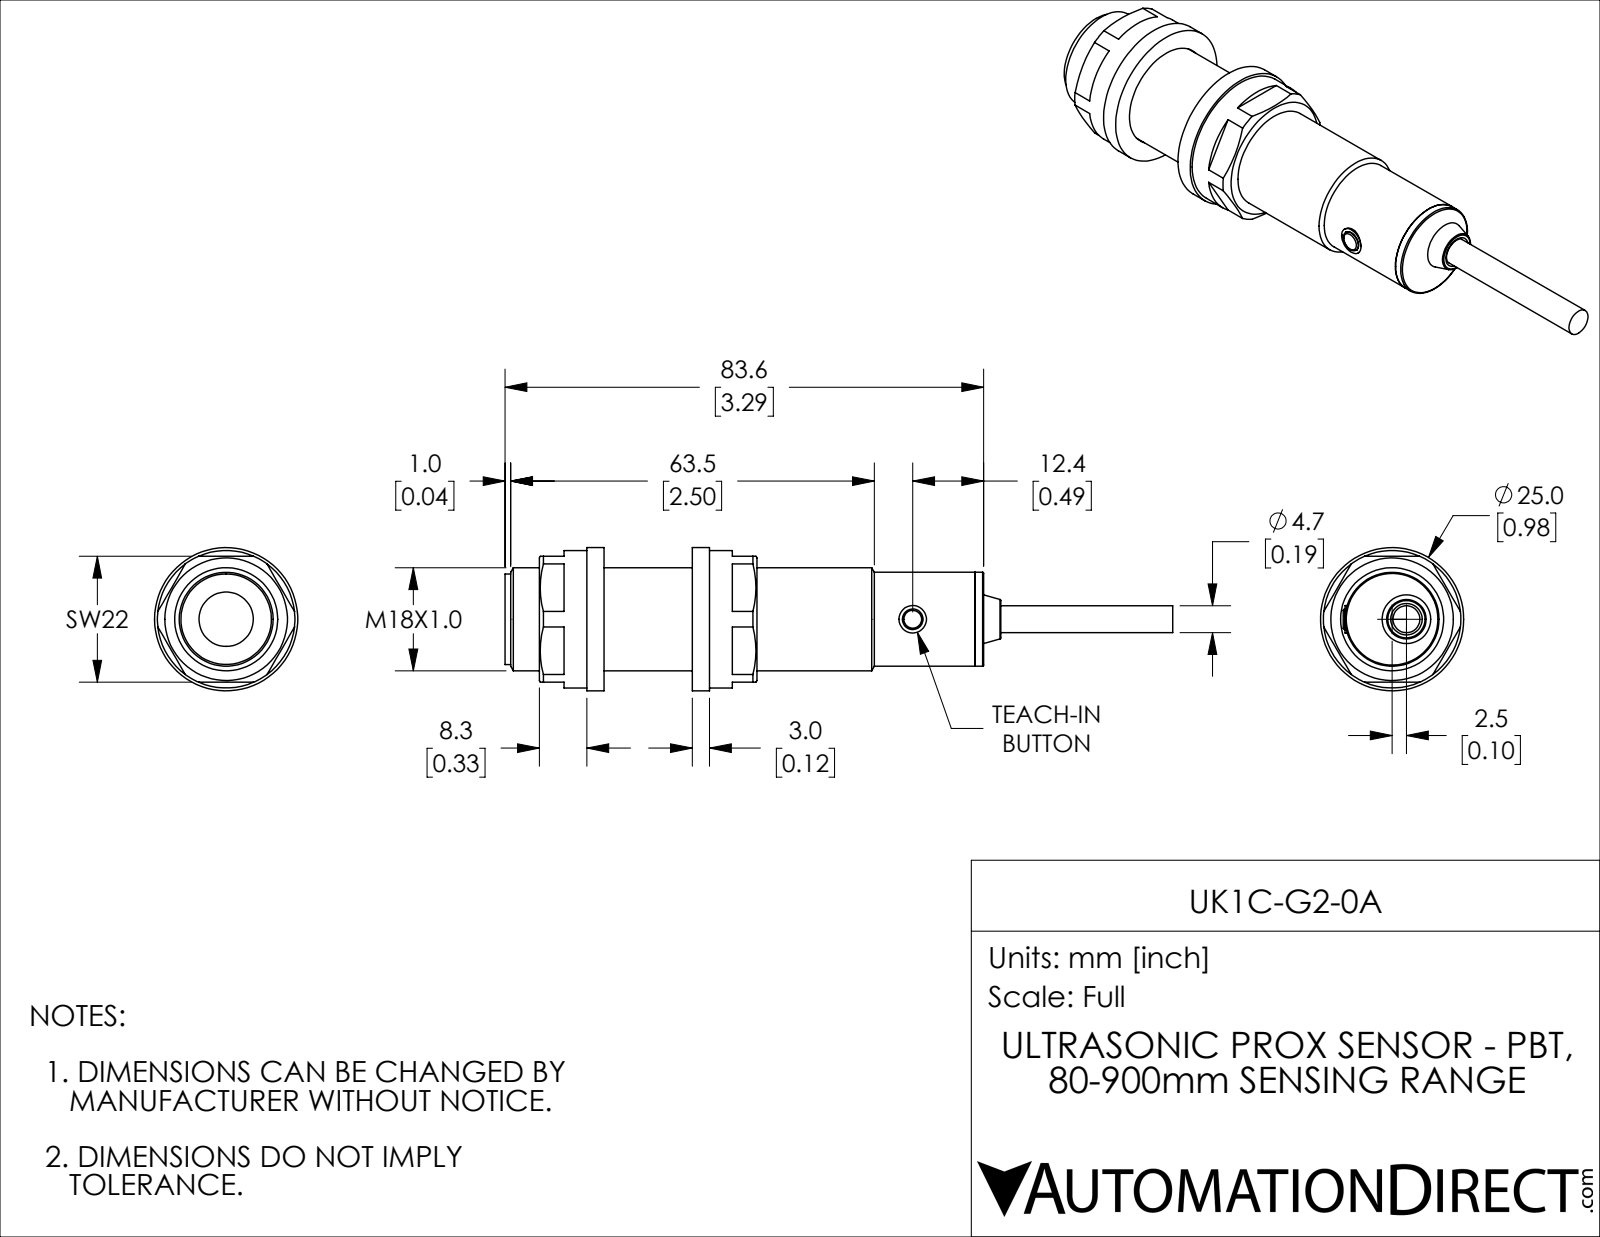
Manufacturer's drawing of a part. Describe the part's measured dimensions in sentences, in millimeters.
The part is named "UK1C-G2-0A". Its 3-D file was written by "SolidWorks 2018 (AUTOMOTIVE_DESIGN)". It is 10 solids with 107 faces: 49 planar, 40 cylindrical and 18 other. Overall it measures 116.6 by 25 by 25 millimeters. Its volume is 25 220 cubic millimeters and its surface area 11 419 square millimeters. Round holes: 2 of diameter 4.7, 1 of diameter 3.6, 1 of diameter 9.5, 1 of diameter 18, 1 of diameter 18.2. Round bosses or shafts: 1 of diameter 25, 1 of diameter 24, 1 of diameter 16.4, 1 of diameter 15.8, 1 of diameter 5.4, 1 of diameter 4.8. The main face-to-face distances are 3, 18.4, 21.4, 67.8, 46.4, 13.3, 34.7, 81.1, 16.3, 64.8. The hole center spacings are 2.5.
